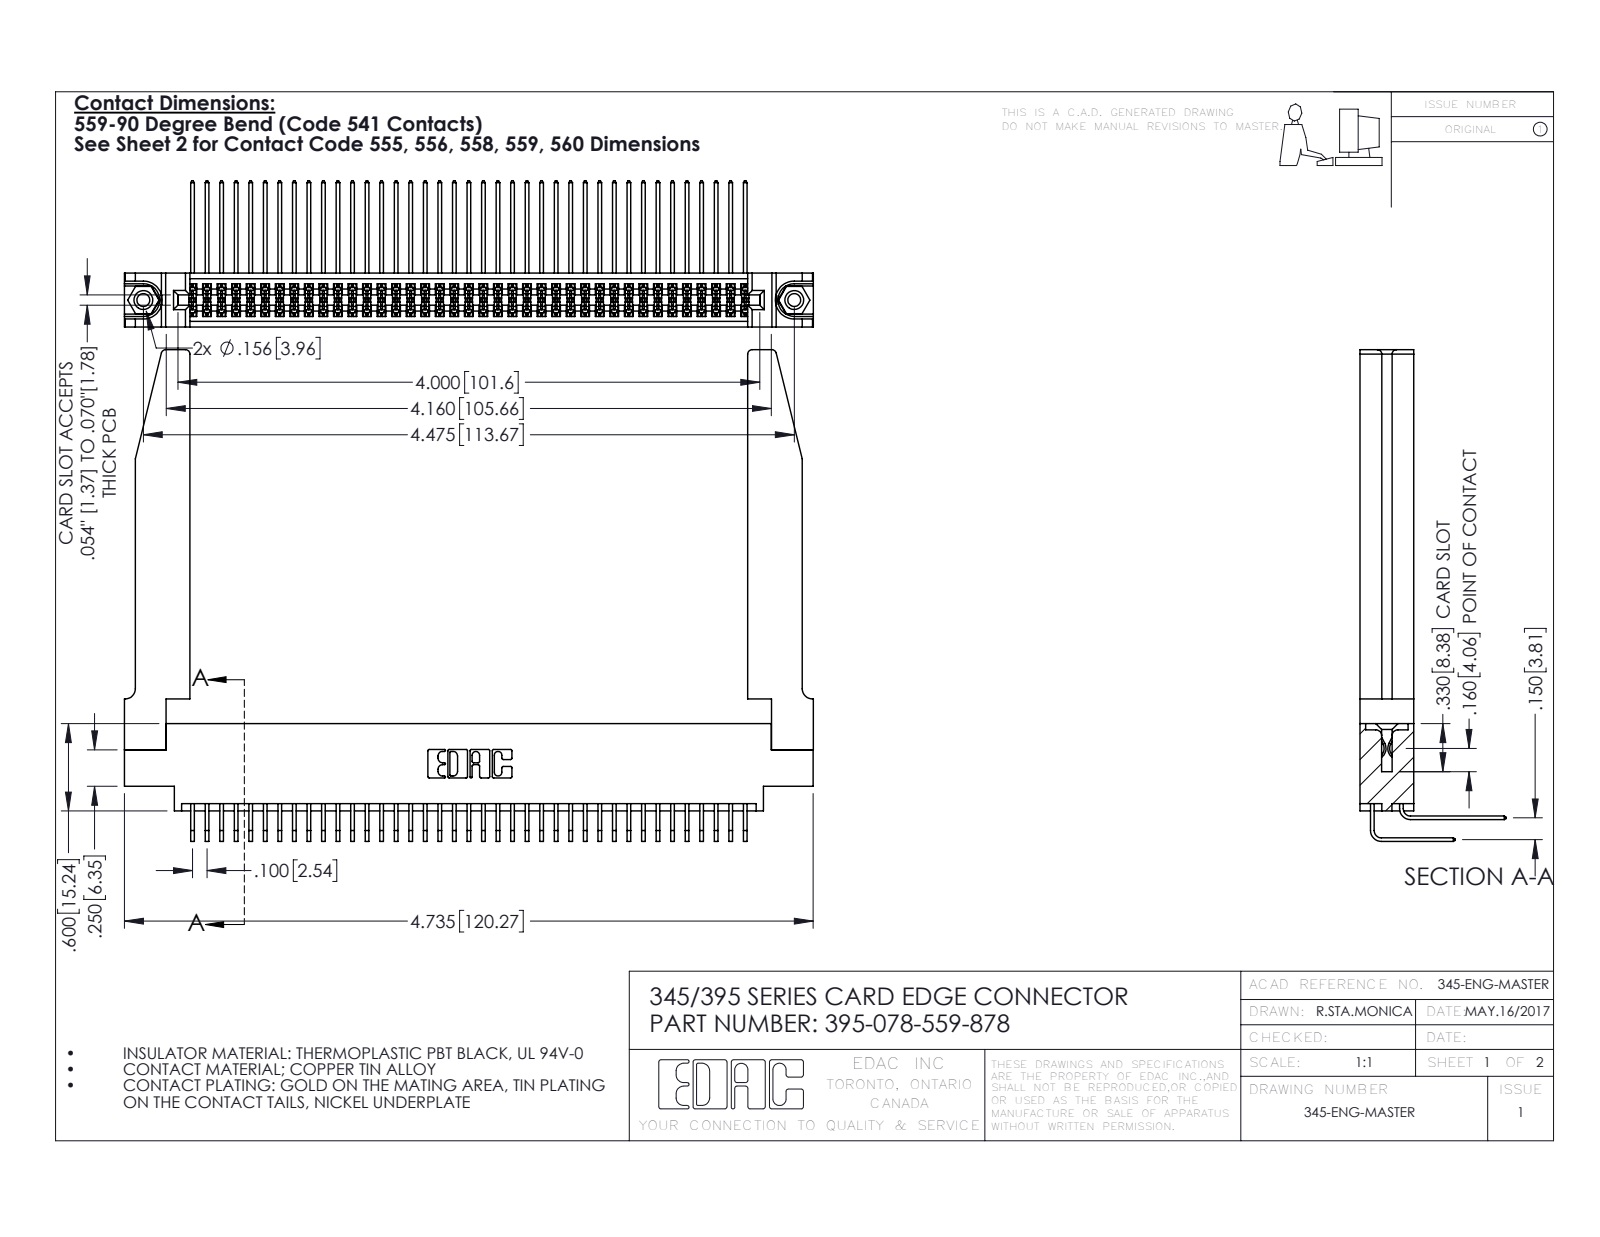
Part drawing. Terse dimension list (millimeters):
name: 345-292-001_558 559 Tail - 1; 345-220-078_345-220-078; 345-292-001_559 Tail - 2; 395-078-559-878 (+2 more)
written by: SolidWorks 2016 (CONFIG_CONTROL_DESIGN)
unit: mm
bodies: 83 solids, 4420 faces (2956 planar, 1412 cylindrical, 52 other)
size: 120.3 × 85.8 × 25.5
volume: 19 760 mm³; area: 26 770 mm²
holes: 2× ⌀2.3, 2× ⌀3.2, 2× ⌀4, 1× ⌀1.6
bosses: 2× ⌀3.9
rounds: 117× R0.2, 22× R0.3, 8× R0.8, 6× R0.2, 6× R0.8, 3× R0.7, 2× R0.4, 2× R0.5
face distances: 9.4, 1.8, 7.6, 5.1, 2.5, 6.9, 0.6, 5.7, 3.8, 4.4
hole spacings: 6.9, 107.7, 113.7
